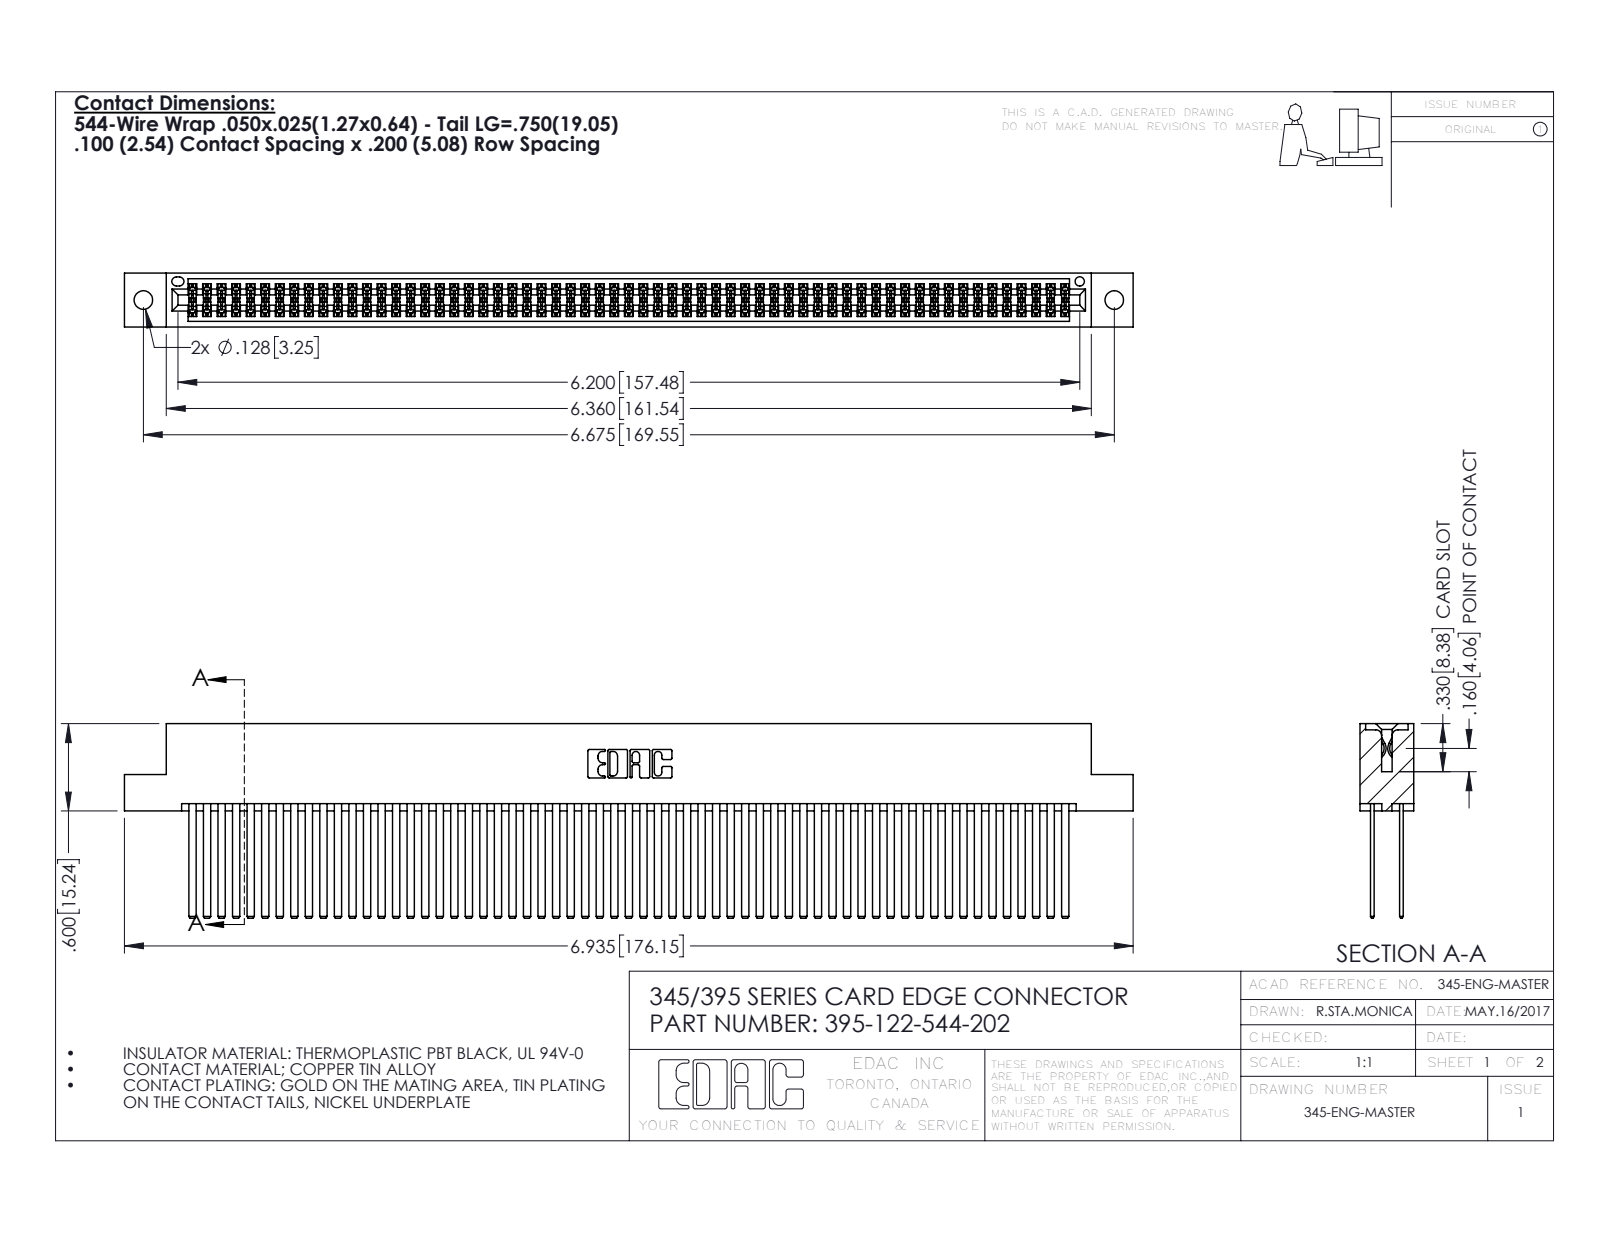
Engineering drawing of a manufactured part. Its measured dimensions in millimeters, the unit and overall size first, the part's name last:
Units: millimetres
Overall size (bounding box): 176.1 × 34 × 9.4
Round holes (diameter × count): ⌀3.3 ×2, ⌀1.6 ×1
Partial cylindrical surfaces — rounded edges, fillets, slot ends (radius × count): R0.2 ×183, R0.3 ×22, R0.2 ×6, R0.8 ×6, R0.7 ×3, R0.4 ×2, R0.5 ×2, R0.6 ×2
Main face-to-face distances: 5.1, 0.6, 7.6, 1.8, 2.5, 6.9, 5.7, 4.4, 9.4, 1.3
Hole centre spacings: 6.9, 163.6, 169.5
Volume: 18 960 mm³ · Surface area: 33 140 mm²
Bodies: 123 solids, 5494 faces (3618 planar, 1876 cylindrical, 0 other)
Part name (STEP PRODUCT): 395-122-544-202; 345-292-001_345-293-144; 345 Part_Flush Mounting Lugs - 0.128 Dia
STEP written by: SolidWorks 2016 (CONFIG_CONTROL_DESIGN)
